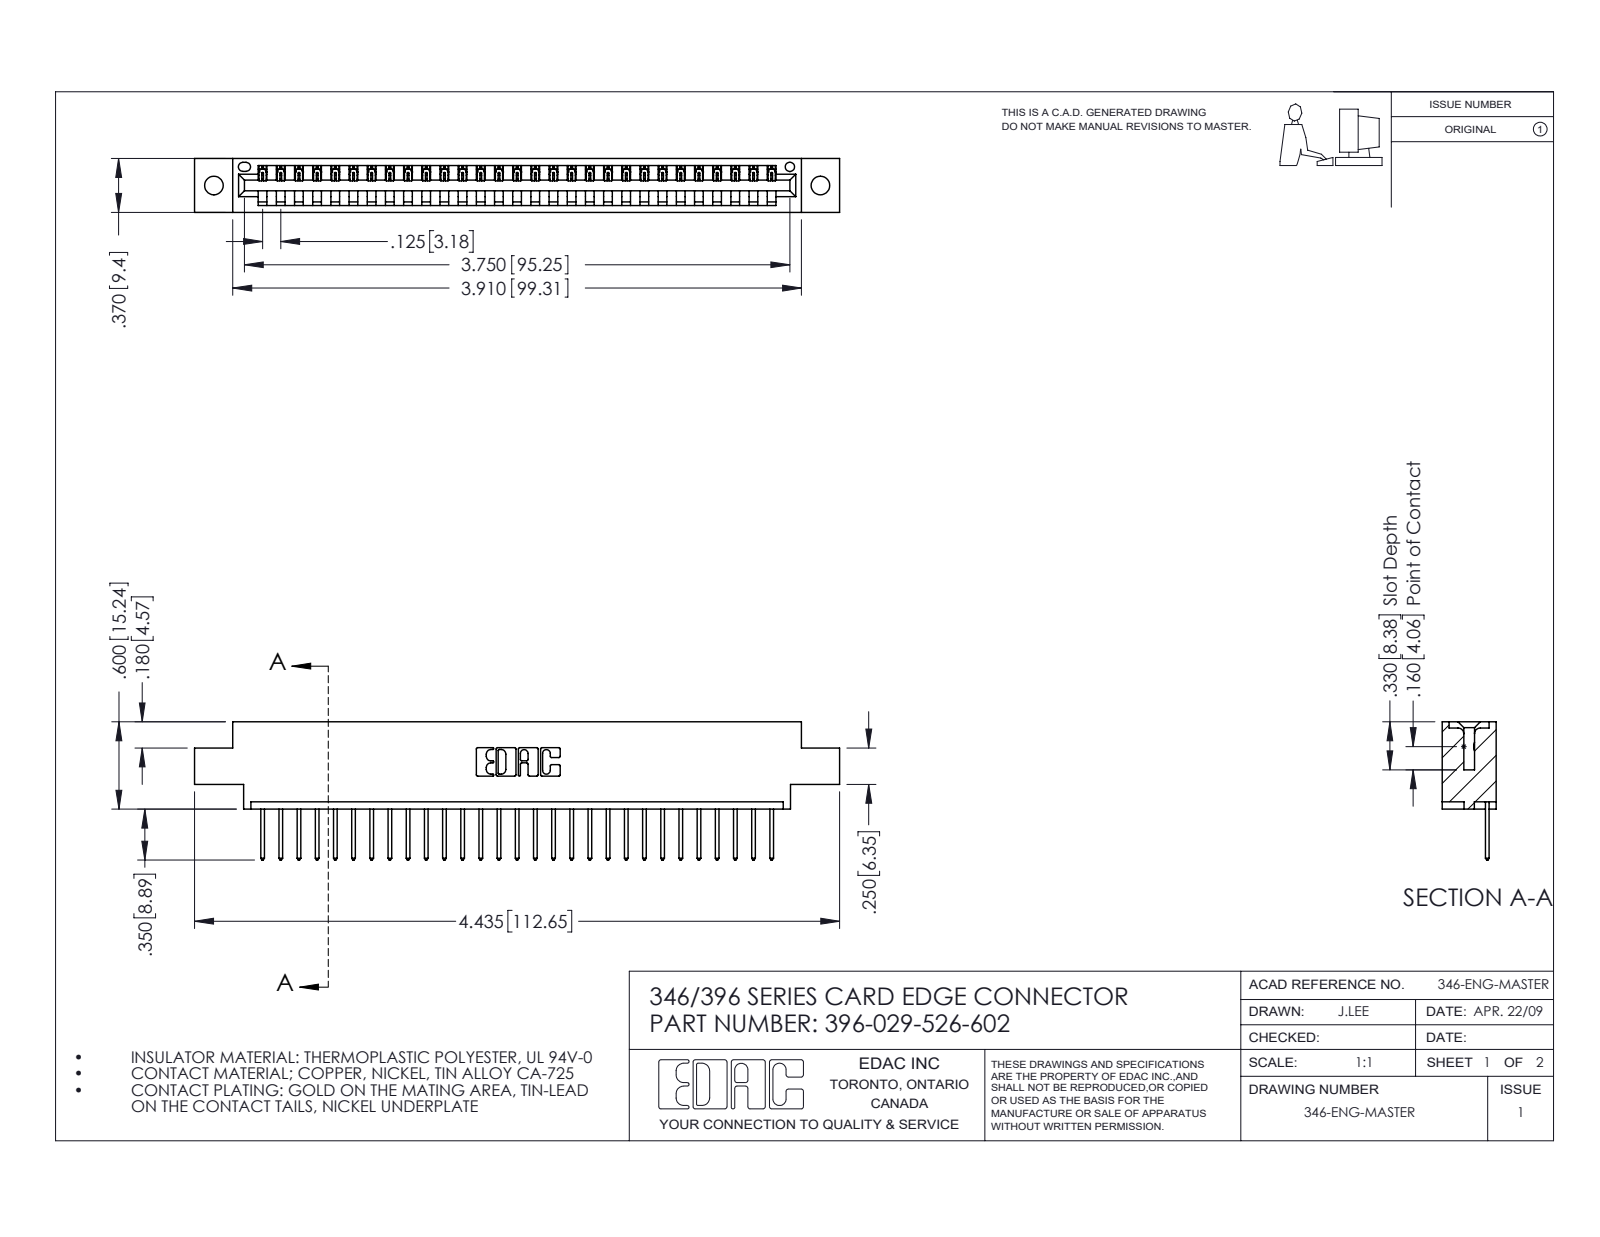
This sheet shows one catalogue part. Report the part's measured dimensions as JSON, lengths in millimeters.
{"part_name": "346 Part_0.170 Offset - 0.128 Dia; 396-029-526-602; 345-292-001_345-293-126", "step_written_by": "SolidWorks 2016 (CONFIG_CONTROL_DESIGN)", "units": "millimeters", "bodies": {"solids": 30, "faces": 1808, "planar": 1240, "cylindrical": 568, "other": 0}, "overall_size": [112.6, 24.1, 9.4], "volume_mm3": 10500, "surface_area_mm2": 12820, "round_holes": [[3.3, 2], [1.6, 1]], "partial_cylinders_radius": [[0.2, 58], [0.3, 58], [0.3, 22], [0.2, 6], [0.8, 6], [0.7, 3], [0.8, 2], [1, 2]], "face_to_face_distances": [1.2, 8.2, 9.4, 6.4, 1.8, 7.6, 0.6, 3.8, 5.6, 2.5], "hole_center_spacings": [6.2, 100.6, 105.9]}
